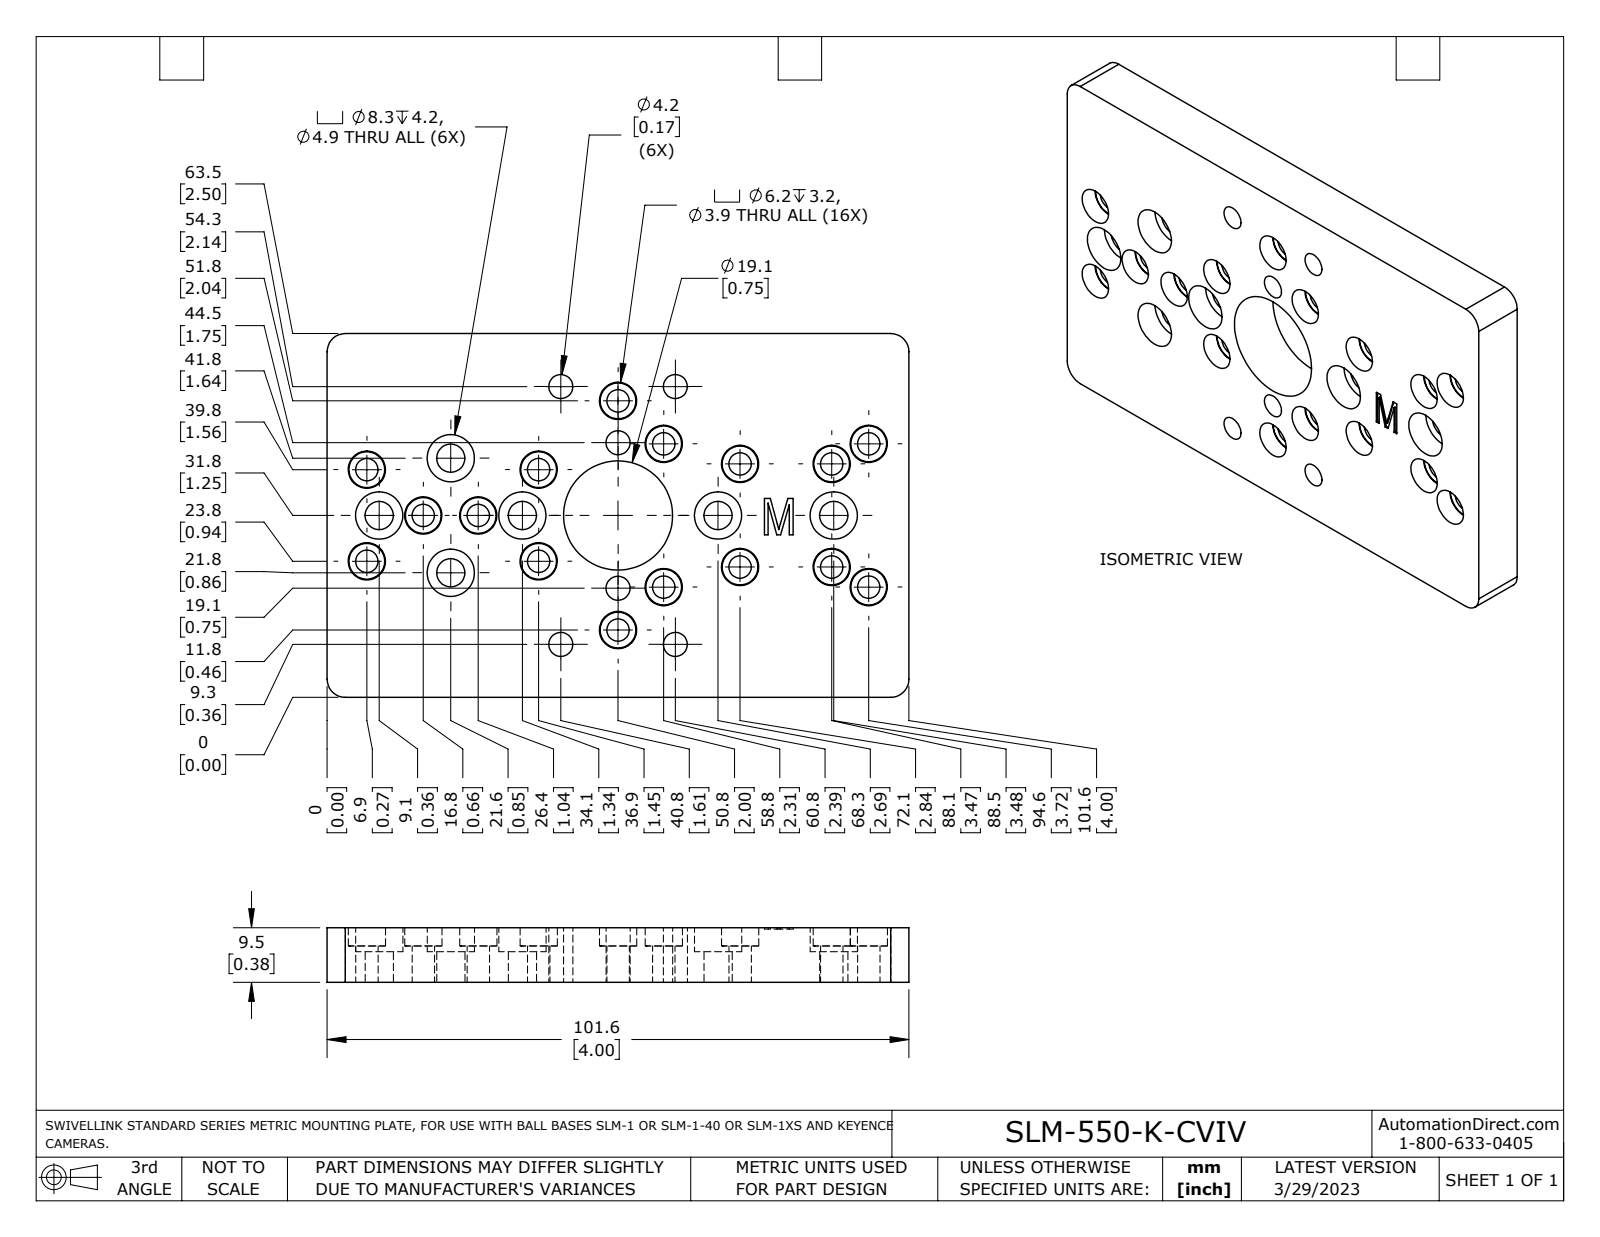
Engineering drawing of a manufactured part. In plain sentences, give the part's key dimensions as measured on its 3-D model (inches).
The part is named "SLM-550-K-CVIV_REV1". Its 3-D file was written by "SolidWorks 2021 (AUTOMOTIVE_DESIGN)". It is 1 solid with 99 faces: 43 planar, 55 cylindrical and 1 other. Overall it measures 4 by 2.5 by 0.375 inches. Its volume is 3.233 cubic inches and its surface area 30.07 square inches. Round holes: 16 of diameter 0.154, 16 of diameter 0.256, 6 of diameter 0.165, 6 of diameter 0.194, 6 of diameter 0.325, 1 of diameter 0.75. Partial cylindrical surfaces (rounded edges, fillets, slot ends): 4 of radius 0.125. The main face-to-face distances are 0.375, 2.5, 4, 0.249, 0.126, 0.21, 0.039, 0.165, 0.365, 0.156. The hole center spacings are 0.63, 0.787, 0.63, 1.215, 1.318, 1.538, 1.719, 0.984.
